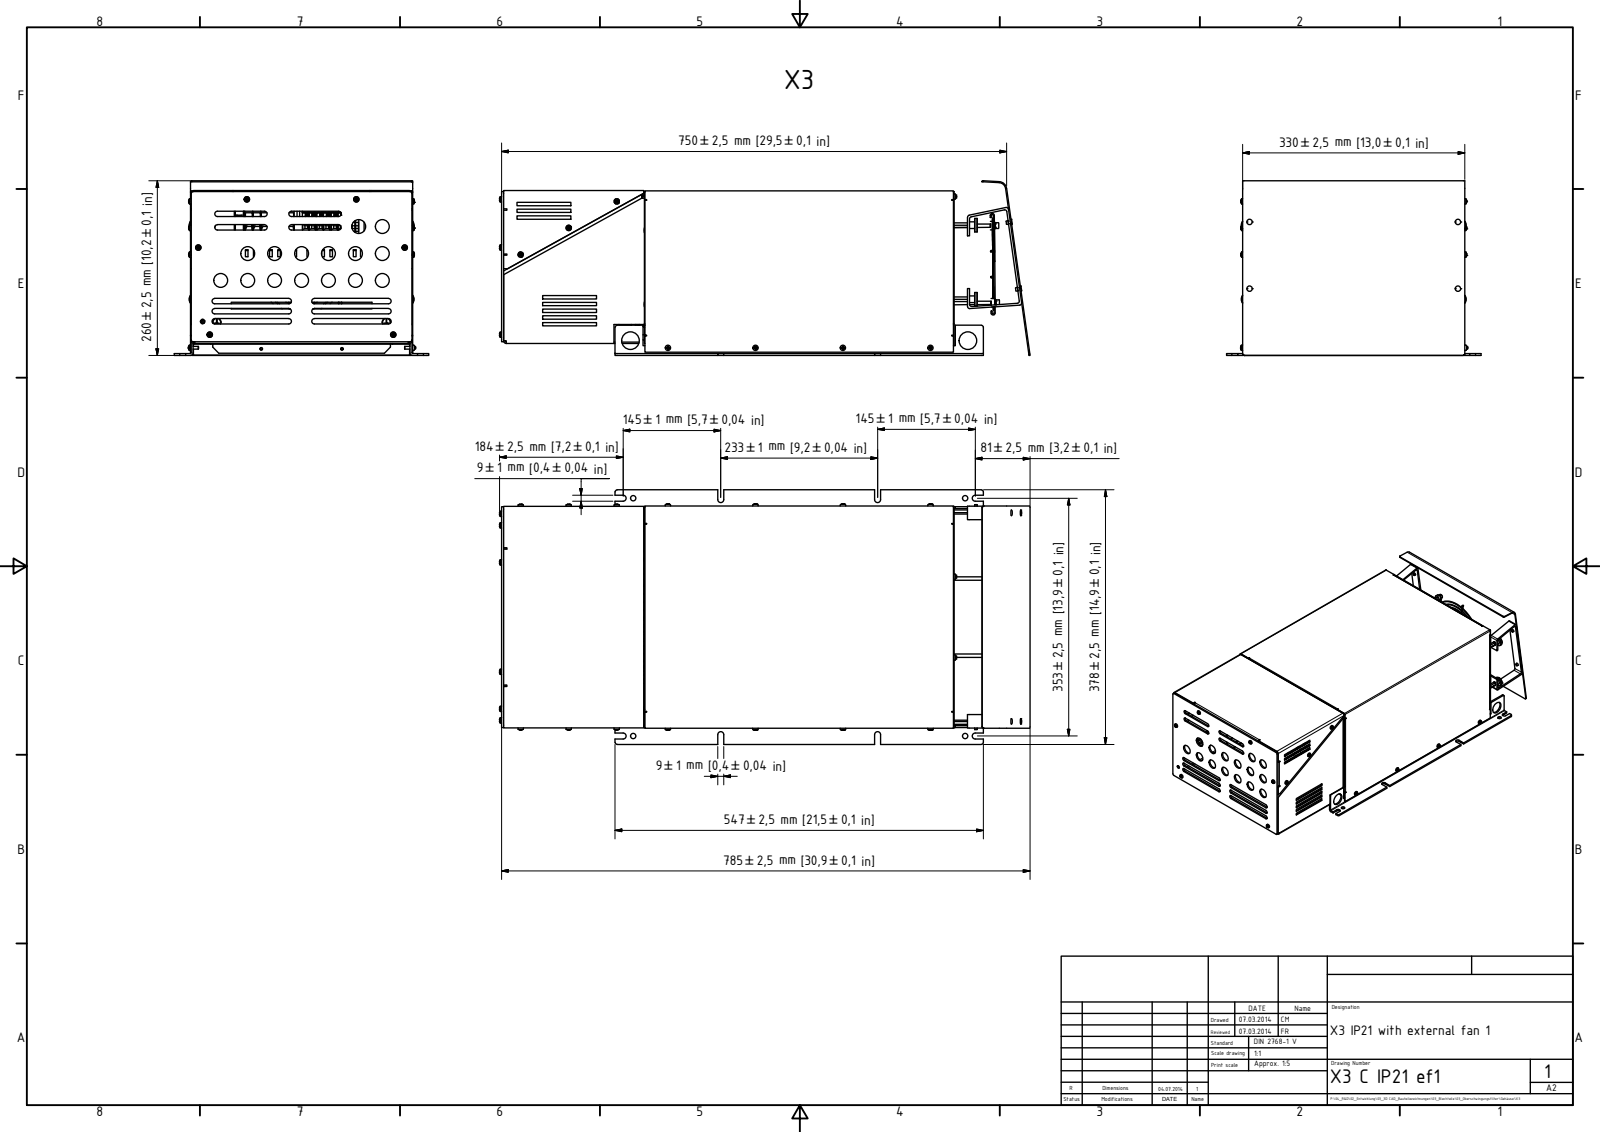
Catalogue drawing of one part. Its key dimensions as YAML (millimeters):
part_name: "10100256 Bodenblech X3; 10100388 Deckel RHF-BG X3-A; 10100387 Anschlussblech RHF-BG X3-A; 10100262 Lüfterblech RHF-BG X3-A (+8 more)"
step_written_by: "Autodesk Inventor 2015 (AUTOMOTIVE_DESIGN)"
units: millimeters
bodies: {solids: 119, faces: 9075, planar: 5309, cylindrical: 2494, other: 1272}
overall_size: [787.95, 378, 259.51]
volume: 2347000
surface_area: 2698000
round_holes:
  - {diameter: 3.24, count: 29}
  - {diameter: 5, count: 25}
  - {diameter: 6.8, count: 19}
  - {diameter: 20.5, count: 15}
  - {diameter: 4, count: 14}
  - {diameter: 6.32, count: 12}
  - {diameter: 7, count: 6}
  - {diameter: 8, count: 6}
  - {diameter: 8.2, count: 6}
  - {diameter: 9.5, count: 6}
  - {diameter: 6, count: 5}
  - {diameter: 6.5, count: 5}
round_bosses_or_shafts:
  - {diameter: 4, count: 26}
  - {diameter: 3.65, count: 13}
  - {diameter: 3.62, count: 11}
  - {diameter: 1.4, count: 8}
  - {diameter: 10, count: 6}
  - {diameter: 8, count: 6}
  - {diameter: 5, count: 6}
  - {diameter: 20, count: 4}
partial_cylinders:
  - {radius: 0.23, count: 112}
  - {radius: 0.5, count: 85}
  - {radius: 1, count: 68}
  - {radius: 0.15, count: 56}
  - {radius: 2, count: 52}
  - {radius: 0.1, count: 45}
  - {radius: 4, count: 40}
  - {radius: 0.1, count: 39}
face_to_face_distances: [1, 2, 3, 329, 328, 459, 1.5, 224.9, 330, 224.5]
hole_center_spacings: [309.5, 21, 120, 100, 130, 11.9, 21.01, 27.33]
